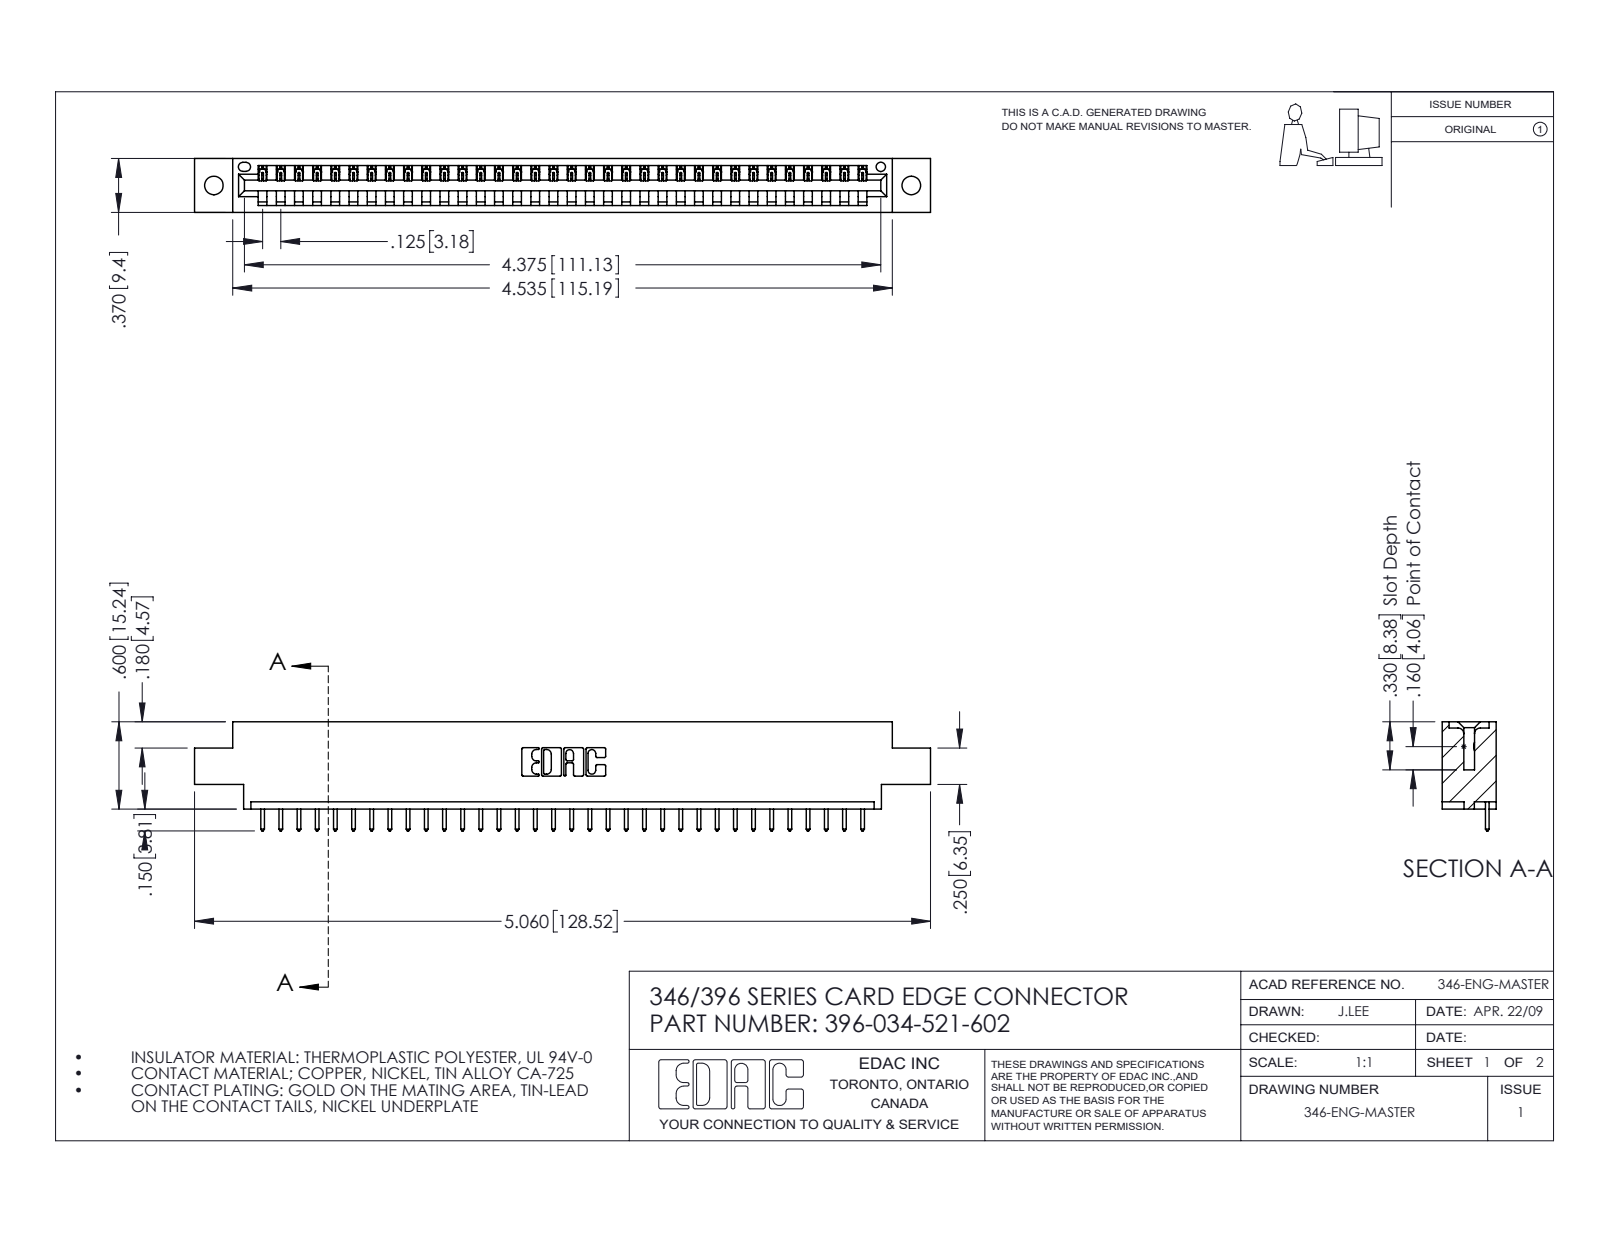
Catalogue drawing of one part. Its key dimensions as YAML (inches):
part_name: "396-034-521-602; 345-292-001_345-293-121; 346 Part_0.170 Offset - 0.128 Dia"
step_written_by: "SolidWorks 2016 (CONFIG_CONTROL_DESIGN)"
units: inches
bodies: {solids: 35, faces: 2098, planar: 1440, cylindrical: 658, other: 0}
overall_size: [5.06, 0.75, 0.37]
volume: 0.73
surface_area: 22.27
round_holes:
  - {diameter: 0.128, count: 2}
  - {diameter: 0.064, count: 1}
partial_cylinders:
  - {radius: 0.006, count: 68}
  - {radius: 0.01, count: 68}
  - {radius: 0.01, count: 22}
  - {radius: 0.007, count: 6}
  - {radius: 0.031, count: 6}
  - {radius: 0.026, count: 3}
  - {radius: 0.031, count: 2}
  - {radius: 0.04, count: 2}
face_to_face_distances: [0.048, 0.322, 0.37, 0.25, 0.072, 0.298, 0.025, 0.148, 0.222, 0.1]
hole_center_spacings: [0.246, 4.587, 4.795]
